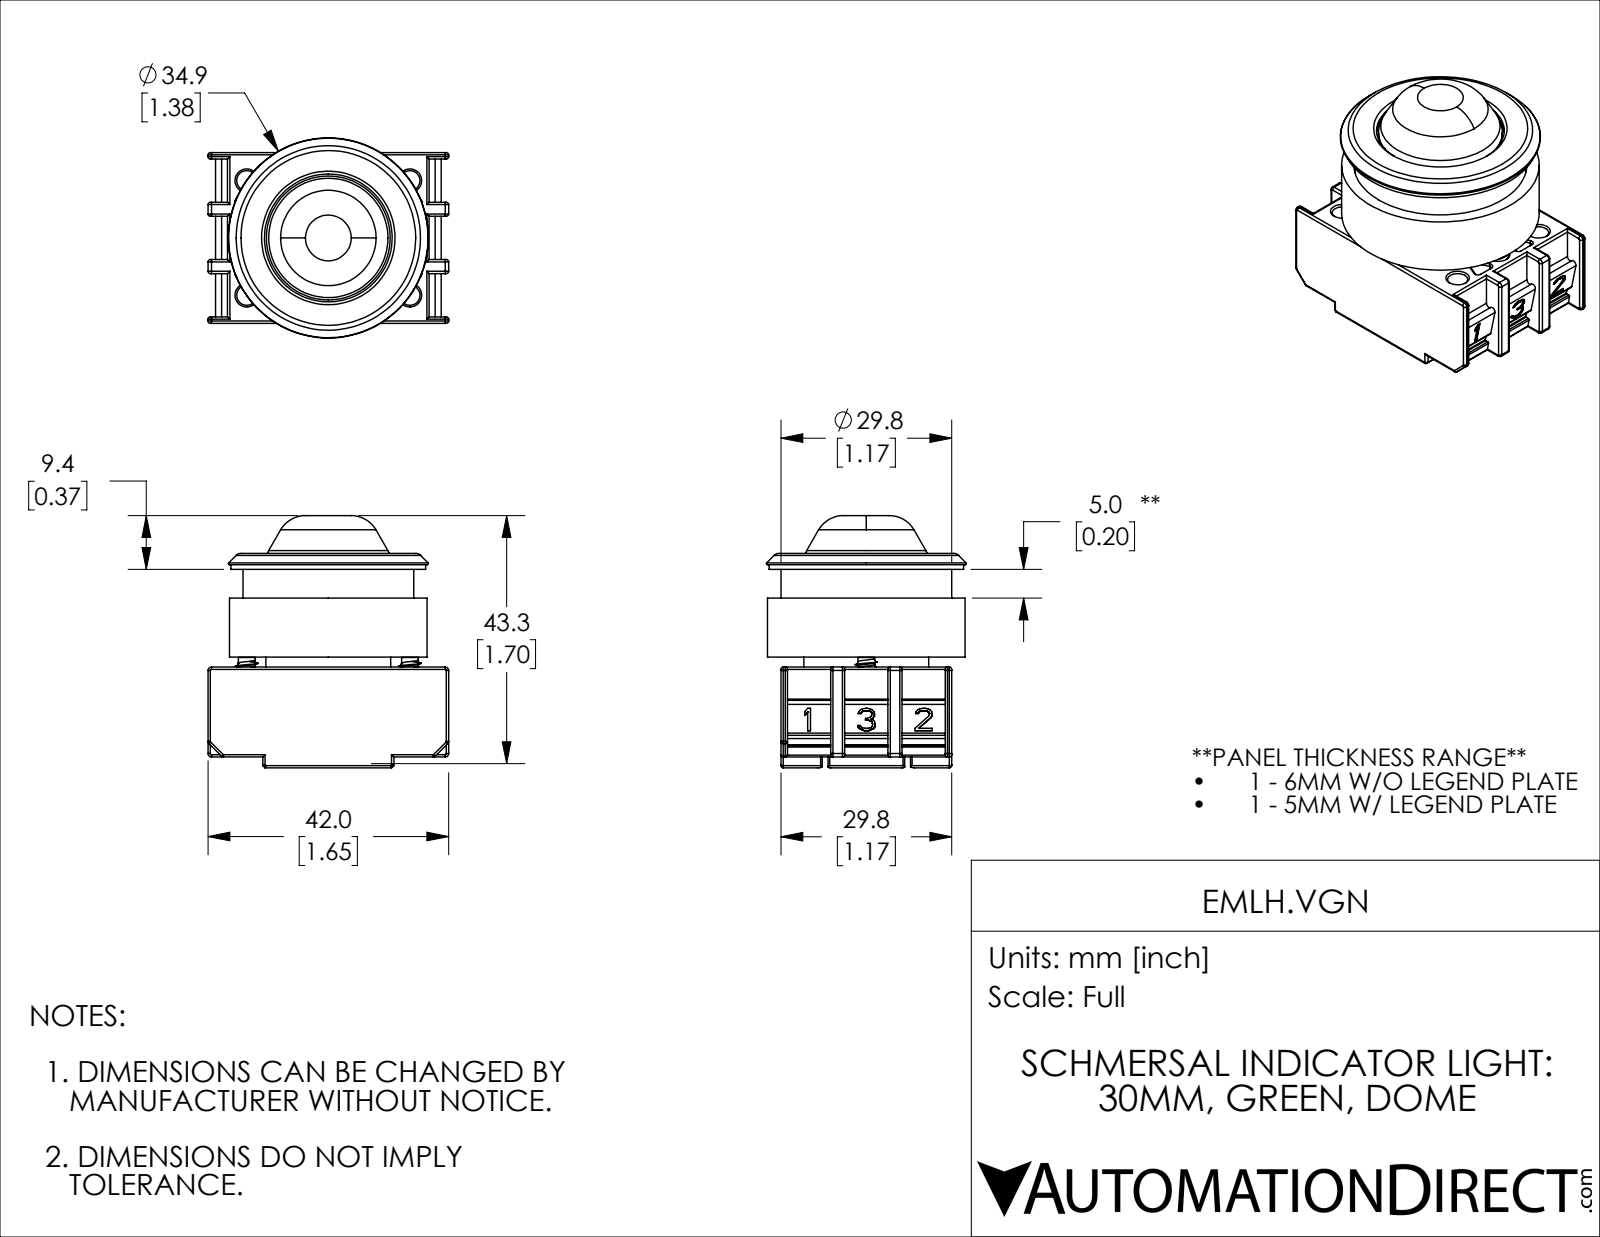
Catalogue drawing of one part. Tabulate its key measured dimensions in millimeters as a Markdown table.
| quantity | value |
| --- | --- |
| part name | EMLH.VGN |
| STEP written by | SolidWorks 2019 (CONFIG_CONTROL_DESIGN) |
| units | millimeters |
| bodies | 3 solids, 1622 faces (641 planar, 498 cylindrical, 483 other) |
| overall size | 44.05 × 42 × 34.93 |
| volume | 22 577 mm³ |
| surface area | 22 231 mm² |
| round holes (diameter × count) | 3.5 × 6, 5.15 × 6, 11 × 1, 12.6 × 1, 15 × 1, 18 × 1, 22.3 × 1, 24.2 × 1, 26 × 1, 27 × 1, 30.2 × 1 |
| round bosses / shafts (diameter × count) | 4.8 × 2, 2.93 × 2, 34.5 × 1, 34 × 1, 29.8 × 1, 25.5 × 1, 24.5 × 1, 23.8 × 1 |
| partial cylindrical surfaces (radius × count) | 0.4 × 115, 0.3 × 48, 0.2 × 28, 0.6 × 8, 0.5 × 6, 0.1 × 2, 0.6 × 2, 0.8 × 2 |
| main face-to-face distances | 29.8, 1.75, 1.9, 19.35, 19.85, 18.1, 10, 3.4, 7.8, 4.4 |
| hole center spacings | 10, 17.41, 30.2, 28.5, 14.25, 20, 34.82 |
